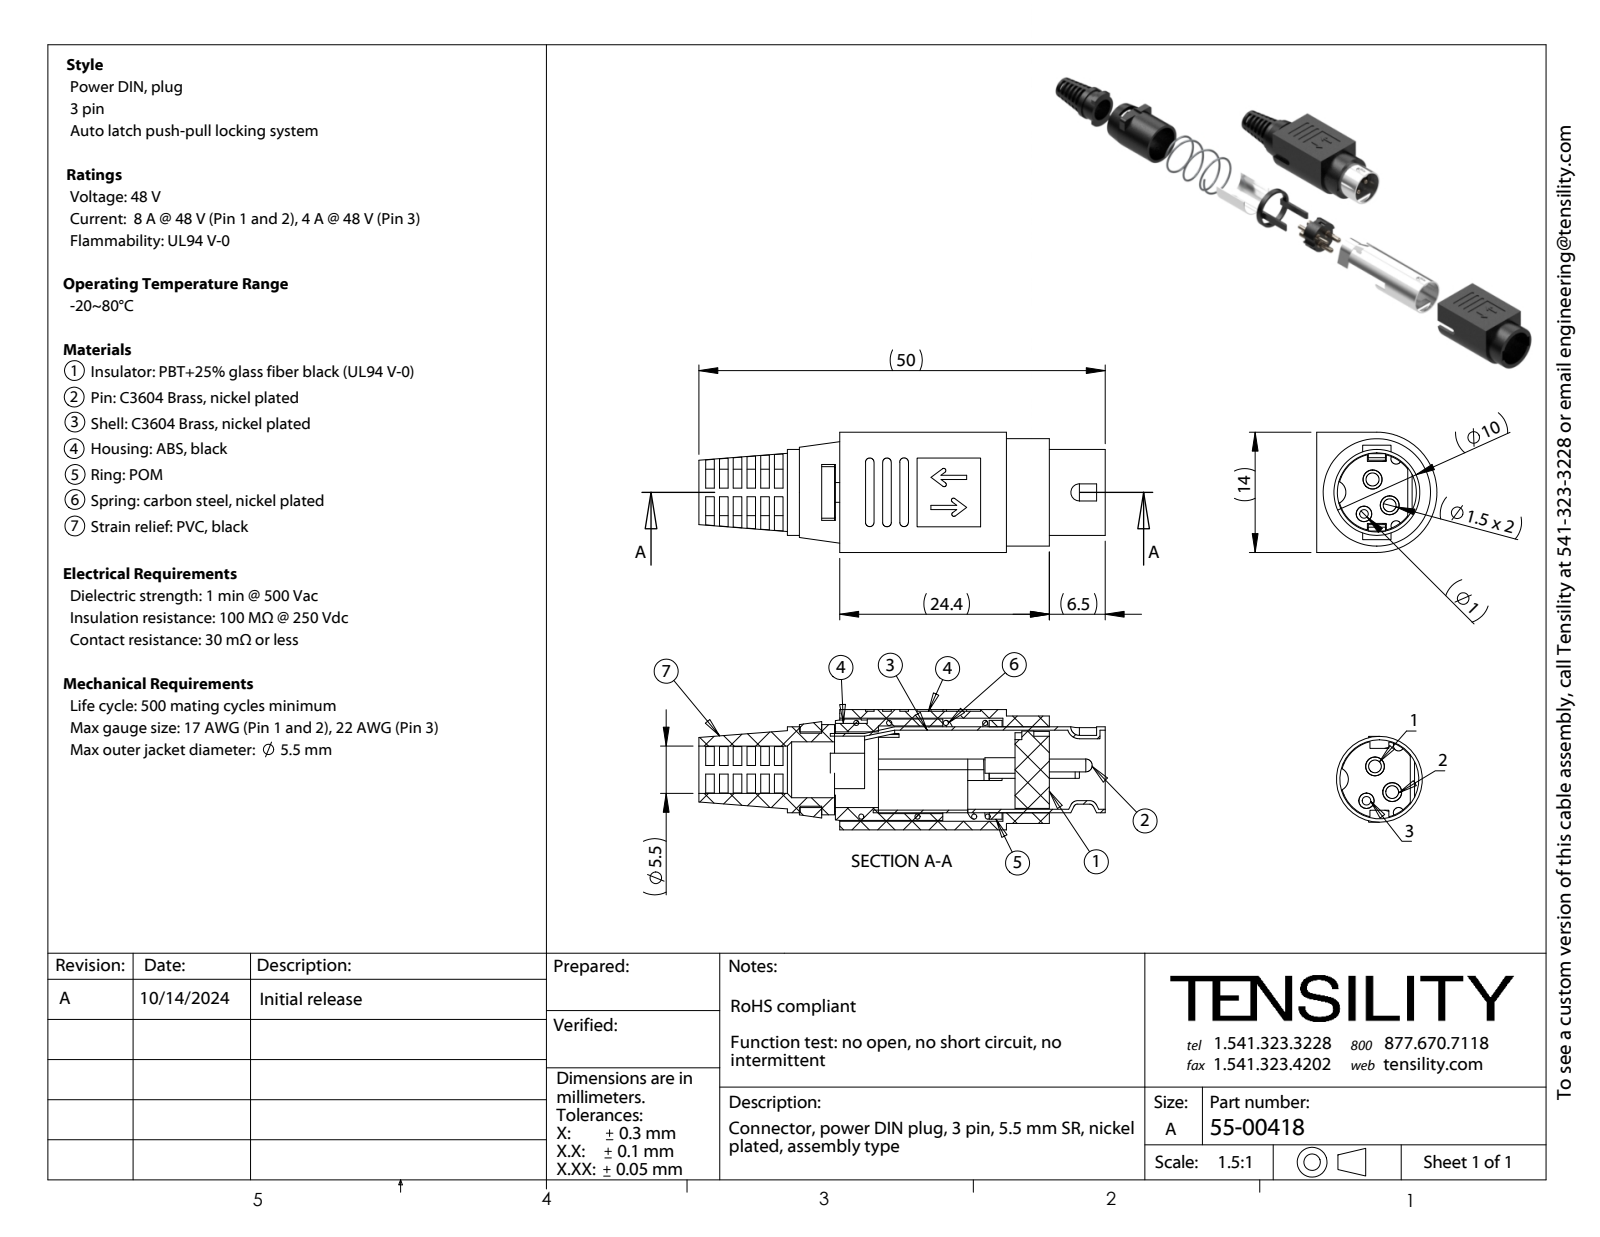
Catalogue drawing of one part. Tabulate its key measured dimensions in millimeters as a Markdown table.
| quantity | value |
| --- | --- |
| part name | 55-00418-10_默认; 55-00418-06_默认; 55-00418-08_默认; 55-00418-04_默认 (+7 more) |
| STEP written by | SolidWorks 2025 (CONFIG_CONTROL_DESIGN) |
| units | millimeters |
| bodies | 11 solids, 403 faces (266 planar, 111 cylindrical, 26 other) |
| overall size | 47.3 × 14 × 14 |
| volume | 2 697 mm³ |
| surface area | 7 444 mm² |
| round holes (diameter × count) | 1.2 × 2, 0.7 × 1, 5.5 × 1, 6.5 × 1, 8.8 × 1, 9.2 × 1, 10.2 × 1 |
| round bosses / shafts (diameter × count) | 1.8 × 3, 2.2 × 2, 1.5 × 2, 12.5 × 1, 11.8 × 1, 11.5 × 1, 10 × 1, 9 × 1 |
| partial cylindrical surfaces (radius × count) | 0.5 × 8, 1 × 4, 0.6 × 3, 0.25 × 2, 0.25 × 2, 0.9 × 2, 1.4 × 1, 1.5 × 1 |
| main face-to-face distances | 1, 13, 1.6, 1.5, 0.5, 12, 5, 0.6, 5.5, 7 |
| hole center spacings | 1.58, 2.12, 2.92, 3.16, 3.61, 4.12 |
